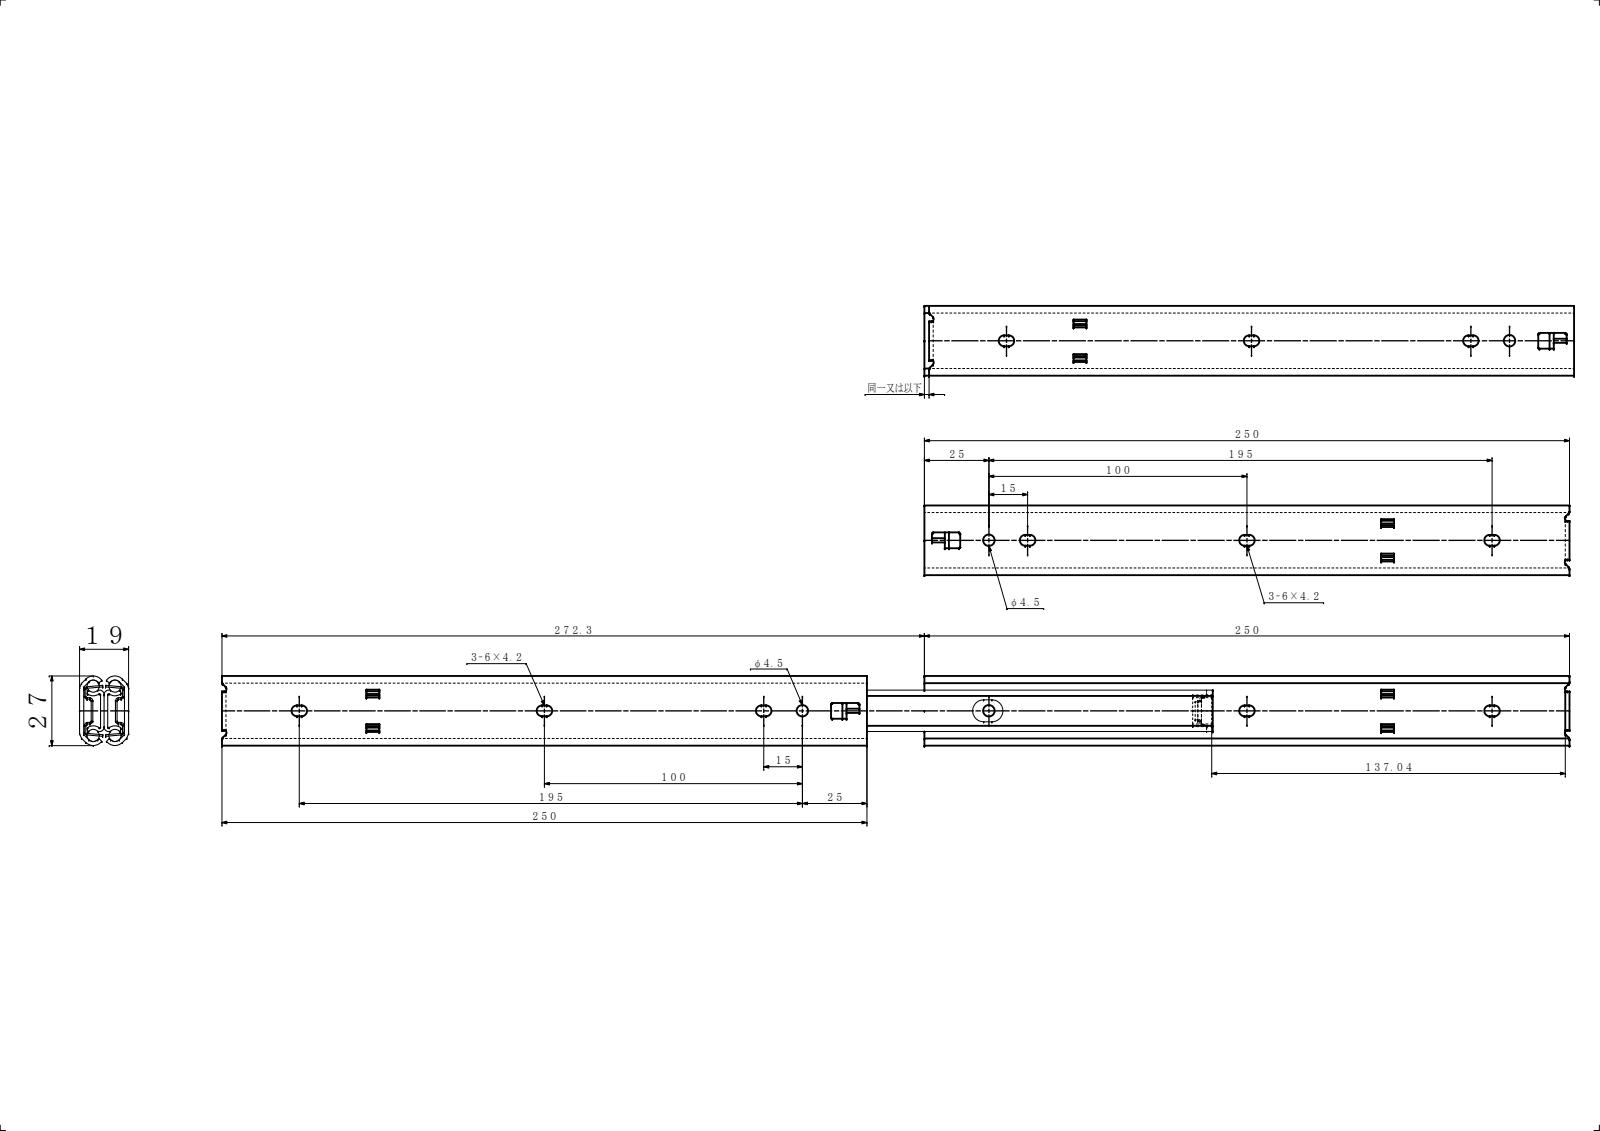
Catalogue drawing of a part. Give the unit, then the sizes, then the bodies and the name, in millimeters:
Units: millimetres
Overall size (bounding box): 522.28 × 27 × 19.1
Round holes (diameter × count): ⌀4.5 ×2
Partial cylindrical surfaces — rounded edges, fillets, slot ends (radius × count): R1 ×38, R2 ×22, R0.1 ×16, R2.1 ×12, R0.3 ×8, R0.5 ×8, R2.38 ×8, R0.28 ×4
Main face-to-face distances: 1.6, 7.95, 9.55, 17.5, 1.4, 8.15, 10.95, 6.55, 9.35, 15.9
Hole centre spacings: 72.28
Volume: 47 861 mm³ · Surface area: 67 257 mm²
Bodies: 8 solids, 398 faces (200 planar, 178 cylindrical, 20 other)
Part name (STEP PRODUCT): SBP1015; SBP1014; IM-2731MC-250; OM-2731MC-250 (+1 more)
STEP written by: SolidWorks 2019 (CONFIG_CONTROL_DESIGN)
